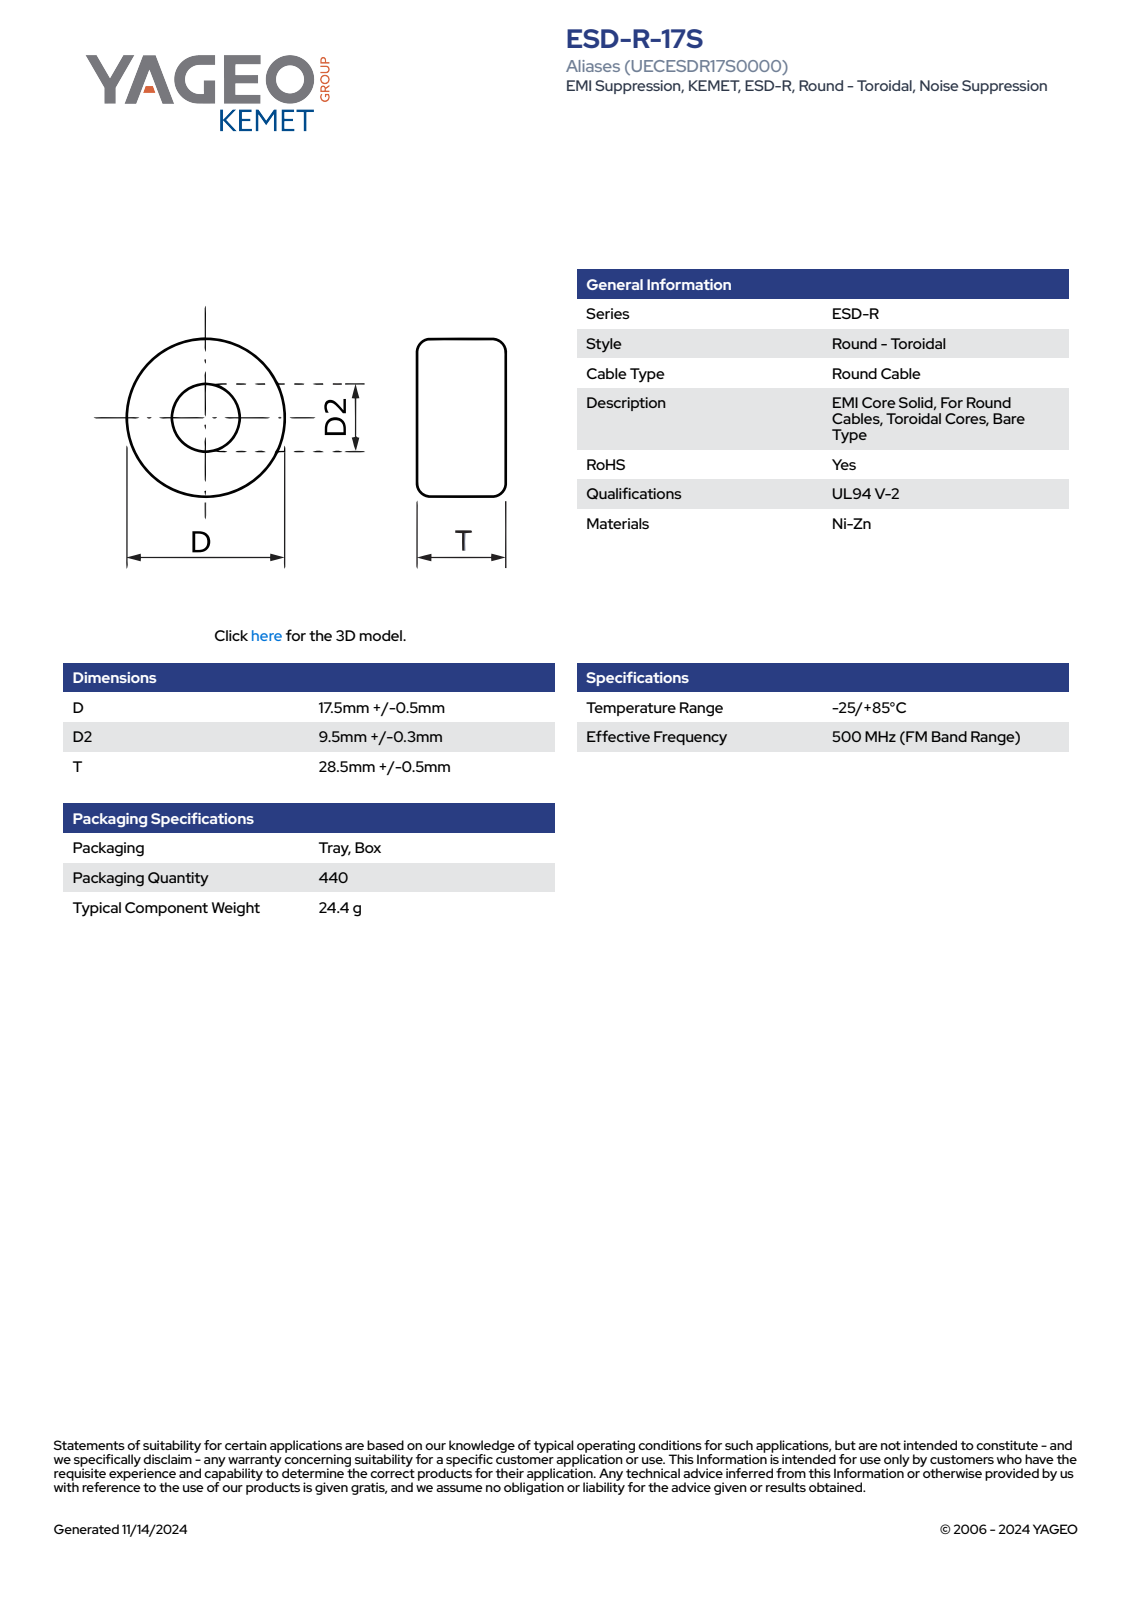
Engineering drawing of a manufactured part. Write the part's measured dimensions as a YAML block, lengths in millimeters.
part_name: "EC_KBC_D18D29.5T29"
step_written_by: "SolidWorks 2021 (AUTOMOTIVE_DESIGN)"
units: millimeters
bodies: {solids: 1, faces: 66, planar: 24, cylindrical: 7, other: 35}
overall_size: [29, 18.01, 18]
volume: 5316
surface_area: 2848
round_holes:
  - {diameter: 9.5, count: 1}
round_bosses_or_shafts:
  - {diameter: 18, count: 1}
partial_cylinders:
  - {radius: 9.01, count: 1}
face_to_face_distances: [29, 13.65, 15.35, 1.7, 0.32, 13.97, 15.03, 1.38, 1.06, 14.71]
